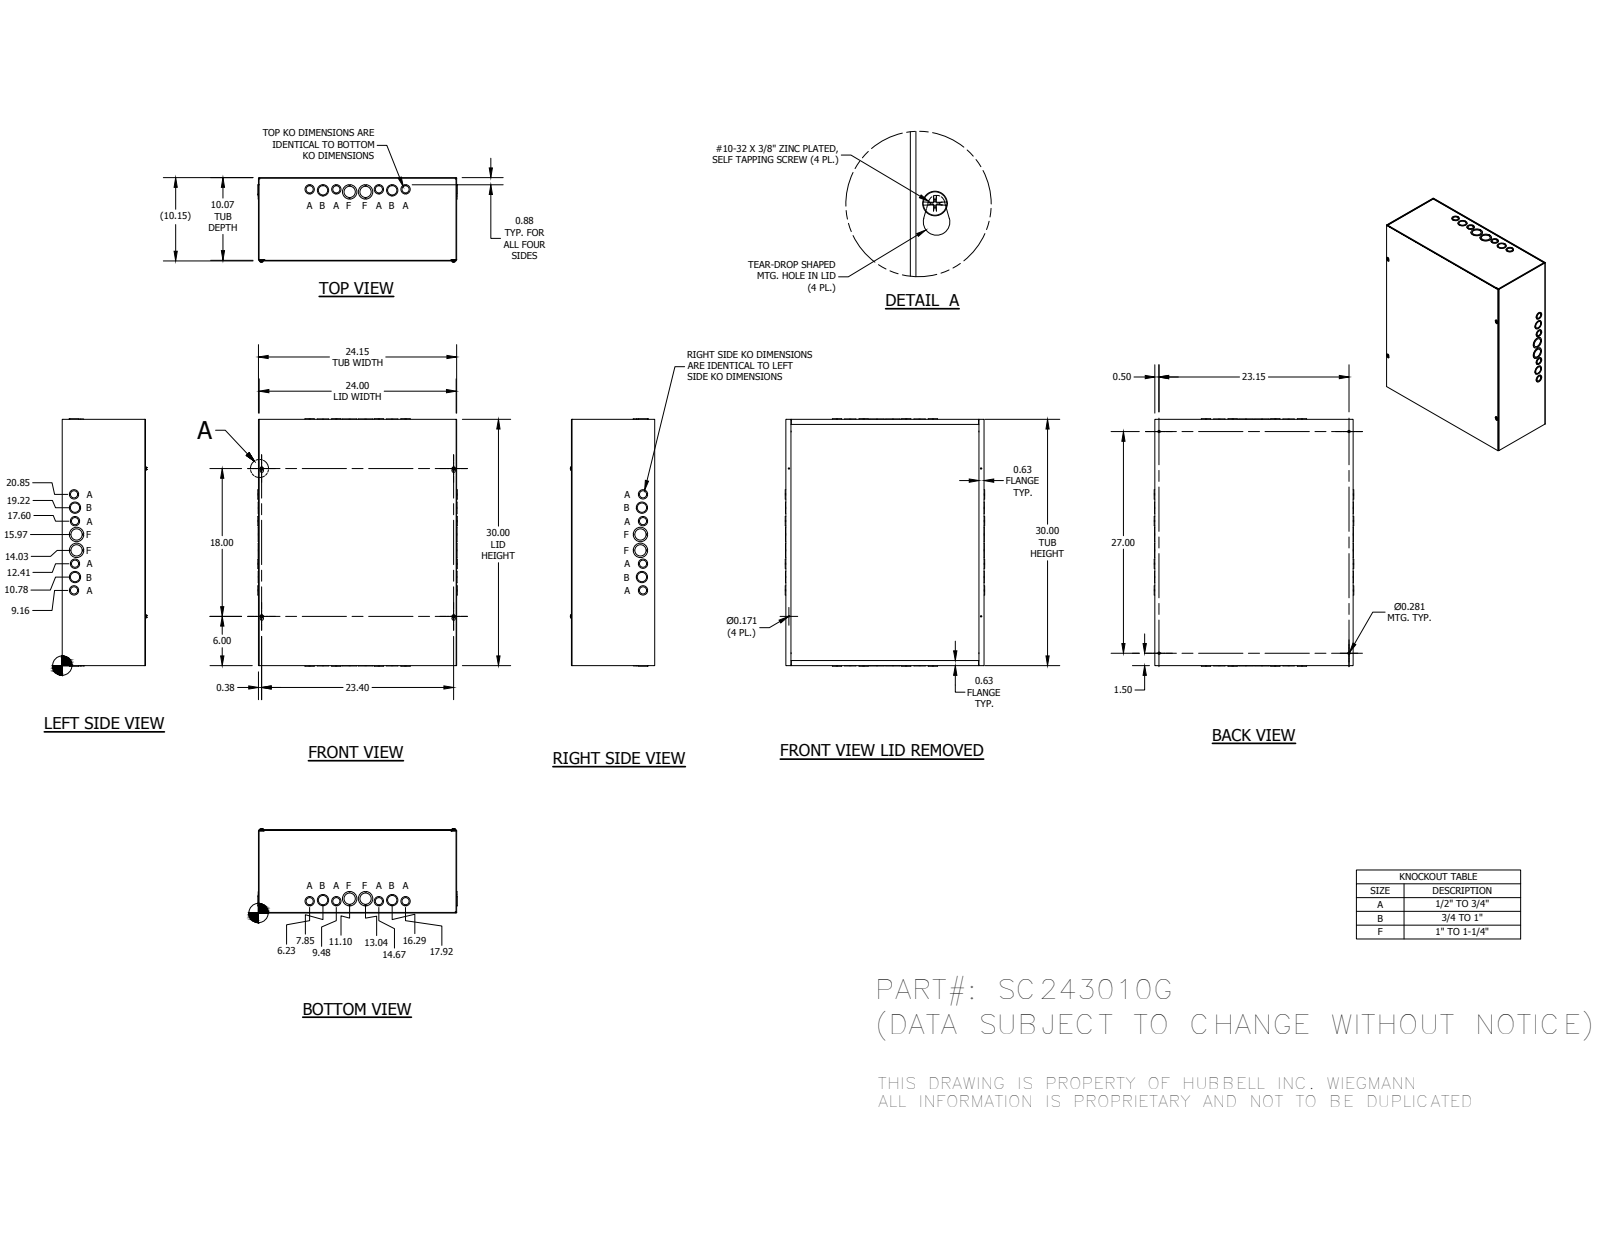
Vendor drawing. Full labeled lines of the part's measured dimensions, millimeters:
Part name (STEP PRODUCT): SC243010GBLR; SC2410GTB; SC2430GLPA; 37214 (+1 more)
STEP written by: Autodesk Inventor 2014 (AUTOMOTIVE_DESIGN)
Units: millimetres
Bodies: 37 solids, 1219 faces (899 planar, 236 cylindrical, 84 other)
Overall size (bounding box): 765.76 × 617.12 × 261.11
Round holes (diameter × count): ⌀28.57 ×14, ⌀22.22 ×10, ⌀34.92 ×8, ⌀4.34 ×4, ⌀7.14 ×4, ⌀44.45 ×4
Round bosses / shafts (diameter × count): ⌀4.83 ×4
Partial cylindrical surfaces — rounded edges, fillets, slot ends (radius × count): R0.4 ×12, R2.28 ×12, R3.17 ×4, R5.16 ×4
Main face-to-face distances: 1.88, 255.88, 254, 257.76, 611.48, 760.12, 609.6, 613.36, 762, 758.24
Hole centre spacings: 41.39, 41.4, 42.03, 82.55, 82.69, 90.9, 114.34, 124.07
